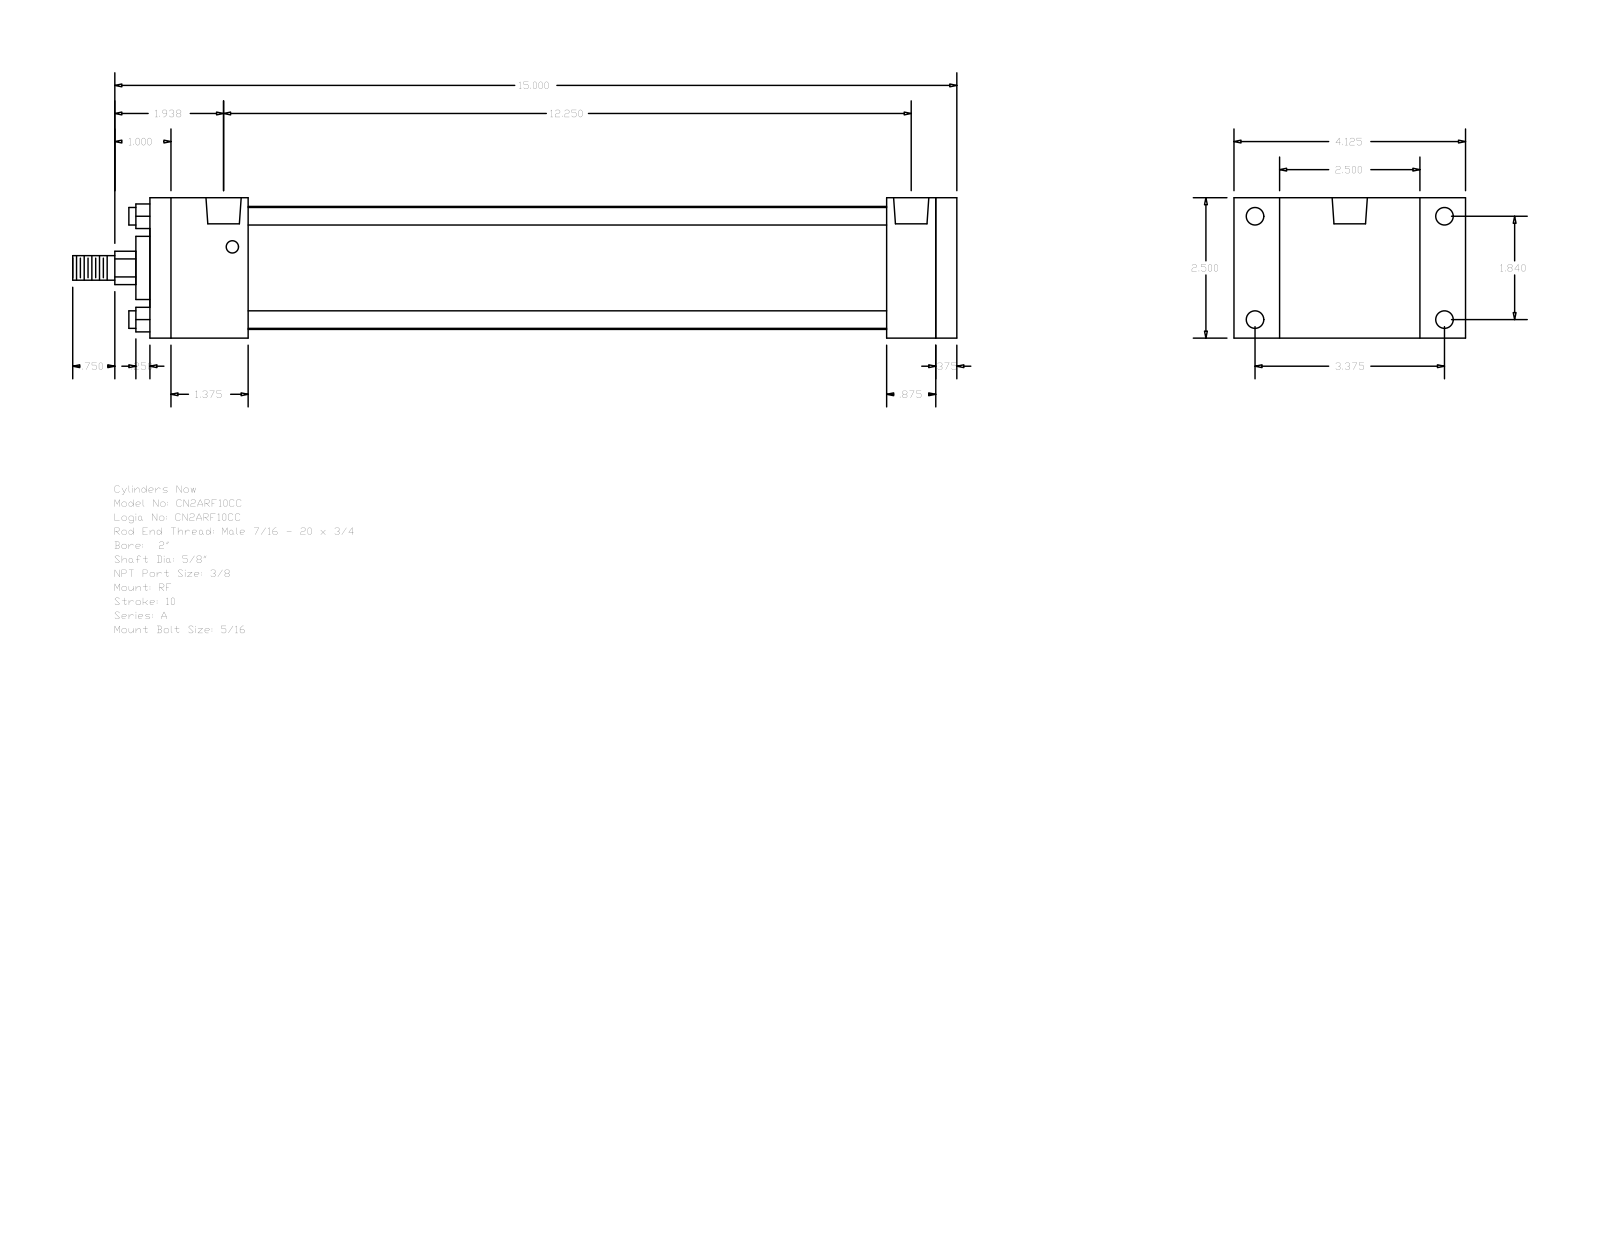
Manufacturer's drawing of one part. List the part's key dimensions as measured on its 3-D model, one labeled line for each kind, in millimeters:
Part name (STEP PRODUCT): A_RF__0200_0.625
STEP written by: GSSL Pune (CONFIG_CONTROL_DESIGN)
Units: millimetres
Bodies: 0 solids, 92 faces (64 planar, 28 cylindrical, 0 other)
Overall size (bounding box): 400.05 × 104.78 × 63.5
Round holes (diameter × count): ⌀5.56 ×4, ⌀7.94 ×4, ⌀15.93 ×2
Round bosses / shafts (diameter × count): ⌀7.94 ×4, ⌀55.63 ×1, ⌀28.57 ×1, ⌀15.88 ×1, ⌀11.11 ×1
Partial cylindrical surfaces — rounded edges, fillets, slot ends (radius × count): R7.54 ×1
Main face-to-face distances: 63.5, 365.12, 355.6, 9.52, 44.45, 311.15, 320.67, 333.37, 288.92, 22.23
Hole centre spacings: 46.74, 85.72, 97.63, 303.2, 3.97, 3.98, 307.17, 307.18
